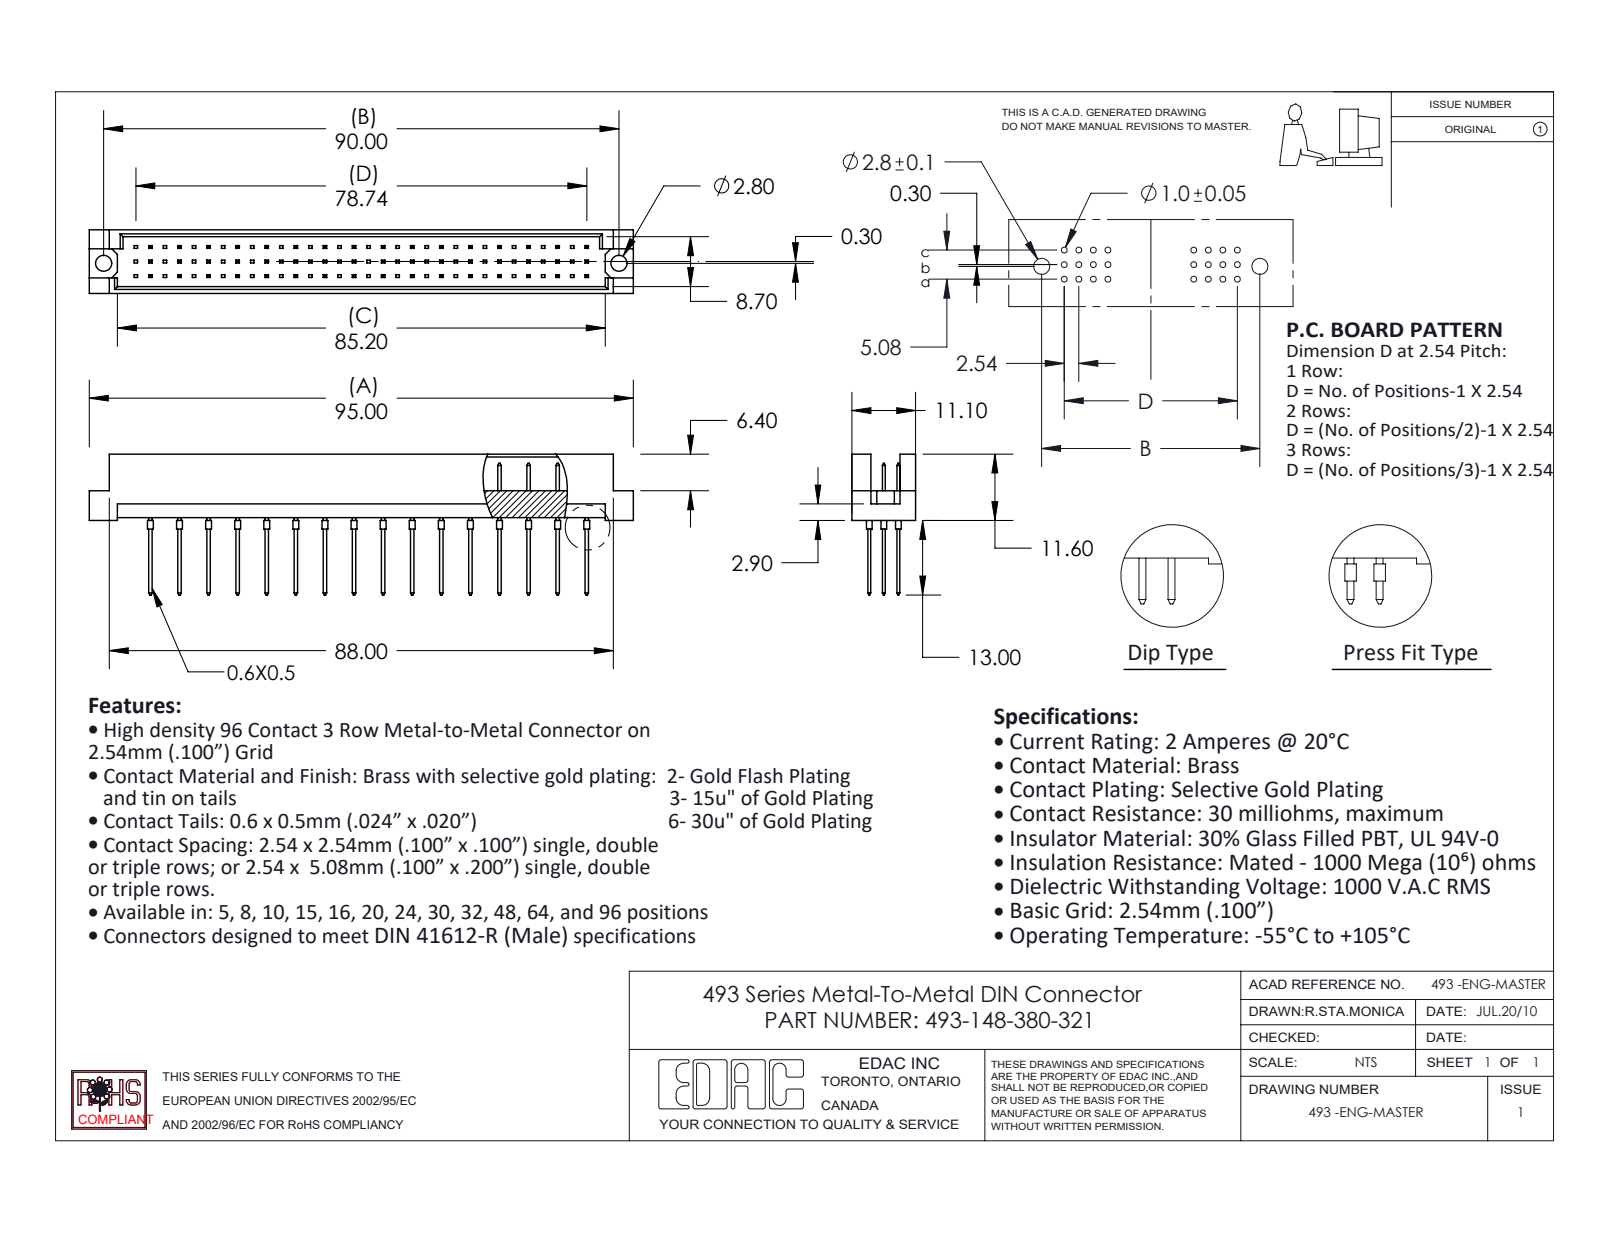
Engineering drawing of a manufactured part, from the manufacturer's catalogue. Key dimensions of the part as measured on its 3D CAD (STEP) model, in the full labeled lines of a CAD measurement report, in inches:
Part name (STEP PRODUCT): 493 Part_96; 493-290_80; 493-148-380-321
STEP written by: SolidWorks 2020 (CONFIG_CONTROL_DESIGN)
Units: inches
Bodies: 49 solids, 1492 faces (1392 planar, 100 cylindrical, 0 other)
Overall size (bounding box): 3.74 × 0.969 × 0.437
Volume: 0.367 in³ · Surface area: 13.95 in²
Round holes (diameter × count): ⌀0.11 ×2
Round bosses / shafts (diameter × count): ⌀0.039 ×48
Main face-to-face distances: 0.047, 0.39, 0.2, 0.1, 0.02, 0.437, 0.343, 0.185, 0.109, 0.128
Hole centre spacings: 3.543
